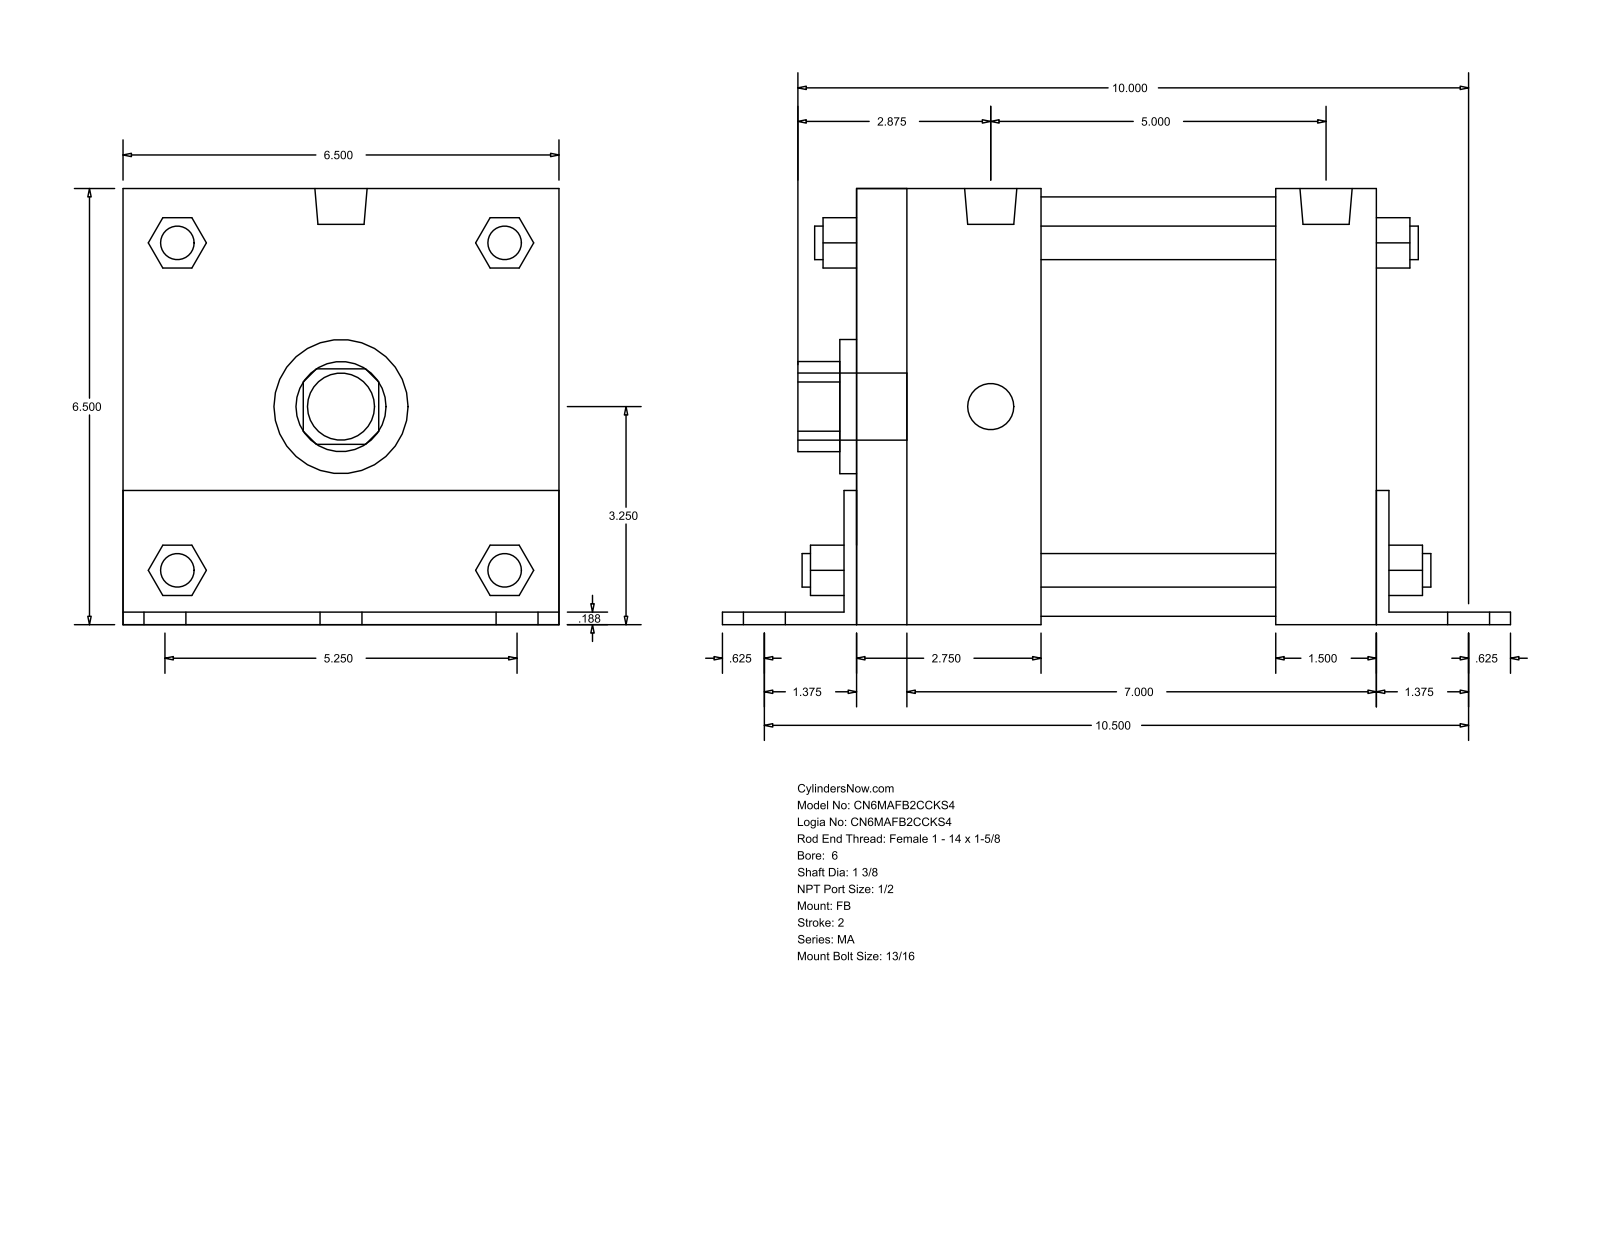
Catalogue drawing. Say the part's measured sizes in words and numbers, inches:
The part is named "MA_FB__0600_1.375". Its 3-D file was written by "GSSL Pune (CONFIG_CONTROL_DESIGN)". It is 0 solids with 140 faces: 105 planar, 35 cylindrical and 0 other. Overall it measures 11.625 by 6.502 by 6.5 inches. Round holes: 1 of diameter 1.375, 1 of diameter 2, 1 of diameter 6.25. Round bosses or shafts: 6 of diameter 0.813, 4 of diameter 0.687, 4 of diameter 0.5, 2 of diameter 0.778, 1 of diameter 1. Partial cylindrical surfaces (rounded edges, fillets, slot ends): 1 of radius 0.672, 1 of radius 1.262. The main face-to-face distances are 6.5, 0.187, 7.625, 6.502, 0.185, 6.315, 0.188, 1.5, 7.813, 8.
